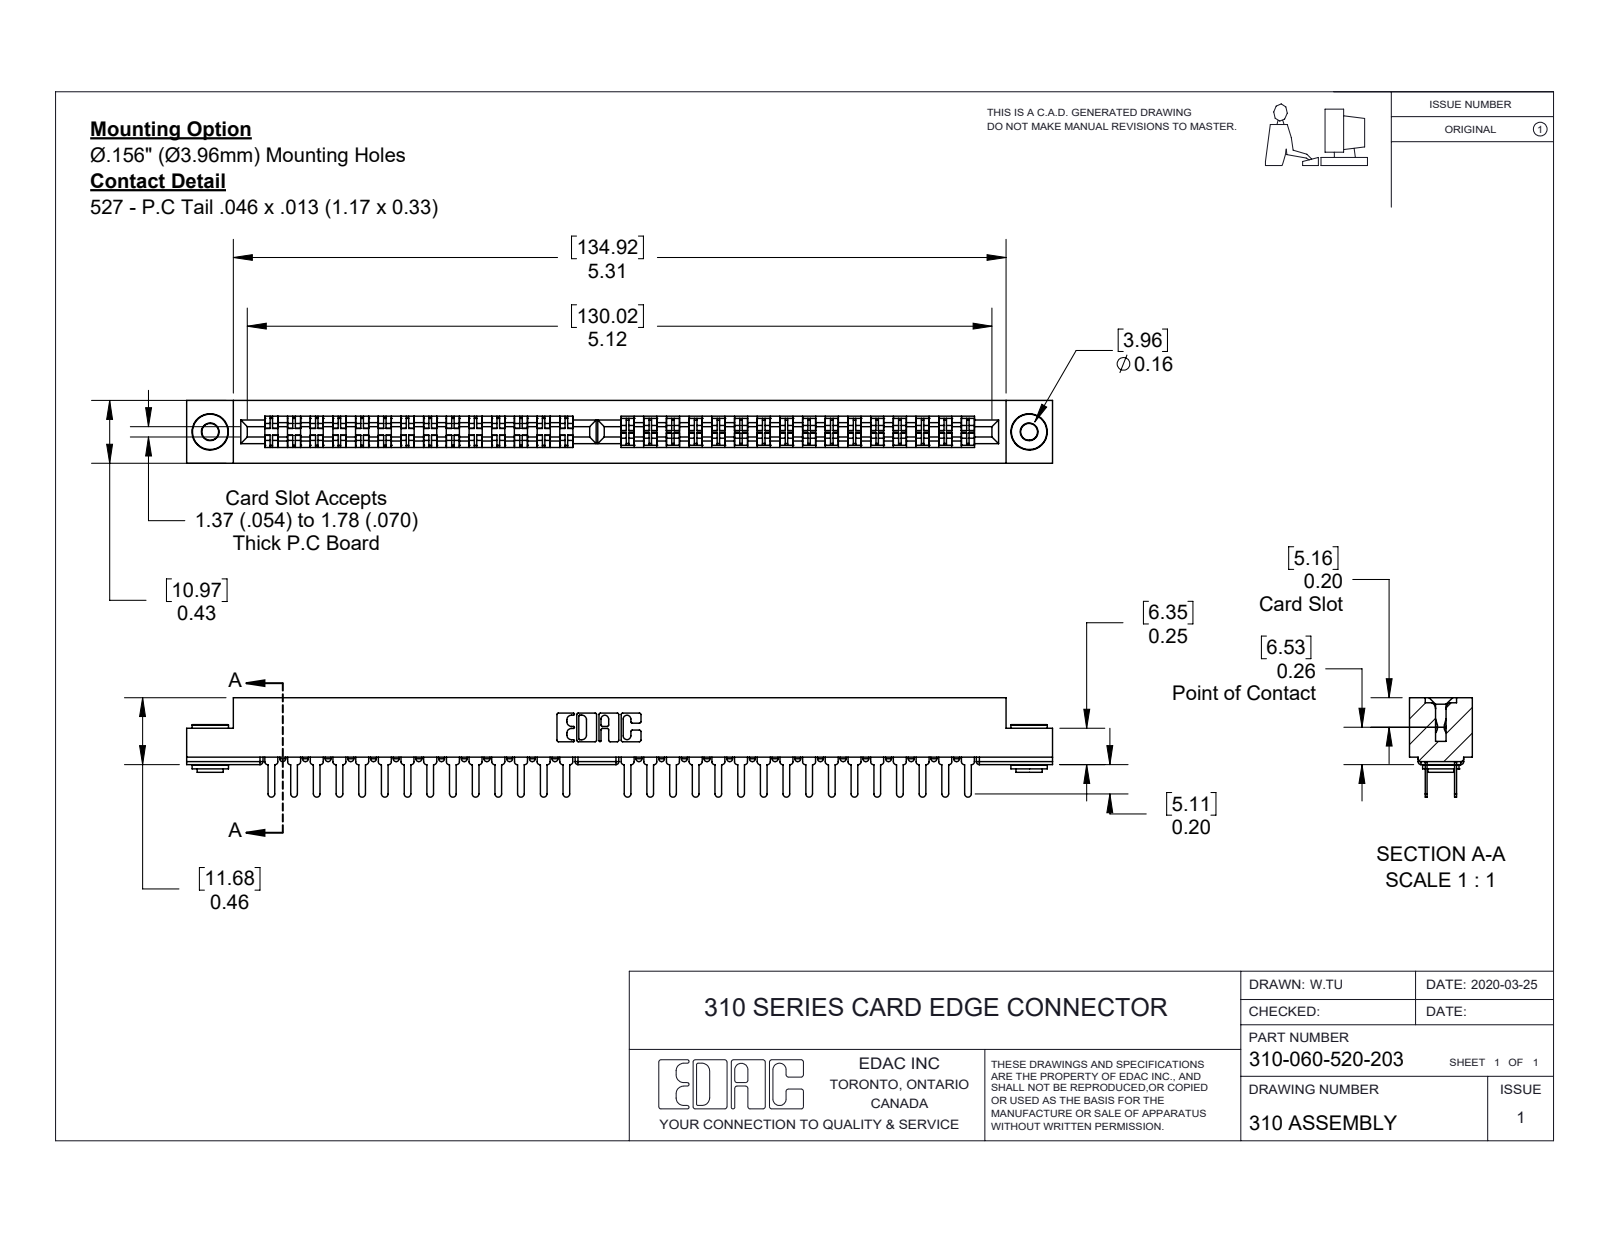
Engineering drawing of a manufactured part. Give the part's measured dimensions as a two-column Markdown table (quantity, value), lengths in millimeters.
| quantity | value |
| --- | --- |
| part name | 310 Part_.116 Hex; 307-290-001_520; 310-060-520-203; 345-250-002_345-250-002-102 |
| STEP written by | SolidWorks 2016 (CONFIG_CONTROL_DESIGN) |
| units | millimeters |
| bodies | 63 solids, 2978 faces (1968 planar, 938 cylindrical, 72 other) |
| overall size | 151.21 × 17.37 × 10.97 |
| volume | 13 056 mm³ |
| surface area | 18 181 mm² |
| round holes (diameter × count) | 2.95 × 2, 3.96 × 2 |
| round bosses / shafts (diameter × count) | 6.35 × 2, 4.57 × 2, 3.45 × 2 |
| partial cylindrical surfaces (radius × count) | 0.51 × 158, 0.58 × 30, 0.25 × 22, 0.17 × 6, 0.8 × 6, 0.3 × 4, 0.64 × 4, 1.19 × 4 |
| main face-to-face distances | 2.76, 8.22, 0.33, 0.38, 4.75, 10.98, 5.46, 3.14, 7.84, 5.08 |
| hole center spacings | 143 |
